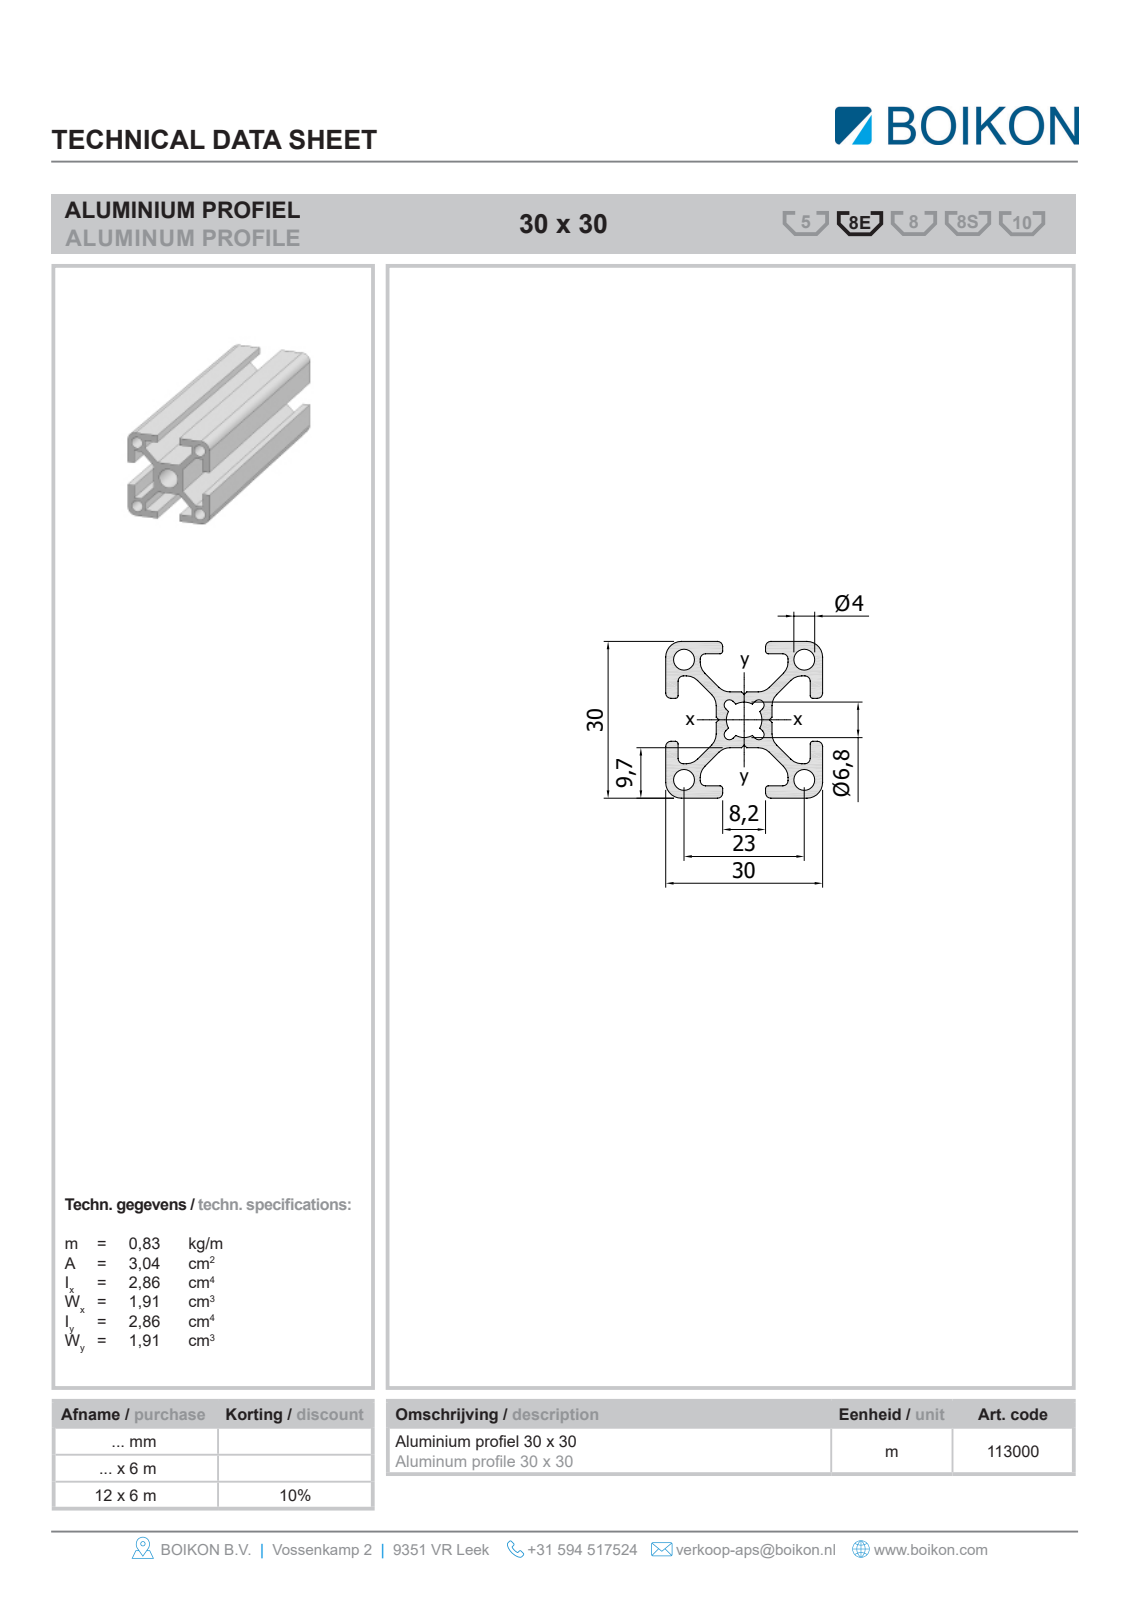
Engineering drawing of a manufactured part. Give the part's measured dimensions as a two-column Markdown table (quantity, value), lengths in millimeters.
| quantity | value |
| --- | --- |
| part name | Root; 11300030x30BOIKON0 |
| STEP written by | HiCAD 2013 1802.4 Build 509 (AUTOMOTIVE_DESIGN) |
| units | millimeters |
| bodies | 1 solid, 55 faces (46 planar, 9 cylindrical, 0 other) |
| overall size | 1000 × 30 × 30 |
| volume | 313 627 mm³ |
| surface area | 314 613 mm² |
| round holes (diameter × count) | 4 × 4, 6.8 × 1 |
| partial cylindrical surfaces (radius × count) | 3 × 4 |
| main face-to-face distances | 2.4, 27.6, 30, 9.7, 20.3, 7.3, 17.9, 2, 6.4, 23.6 |
| hole center spacings | 16.26, 23, 32.53 |
